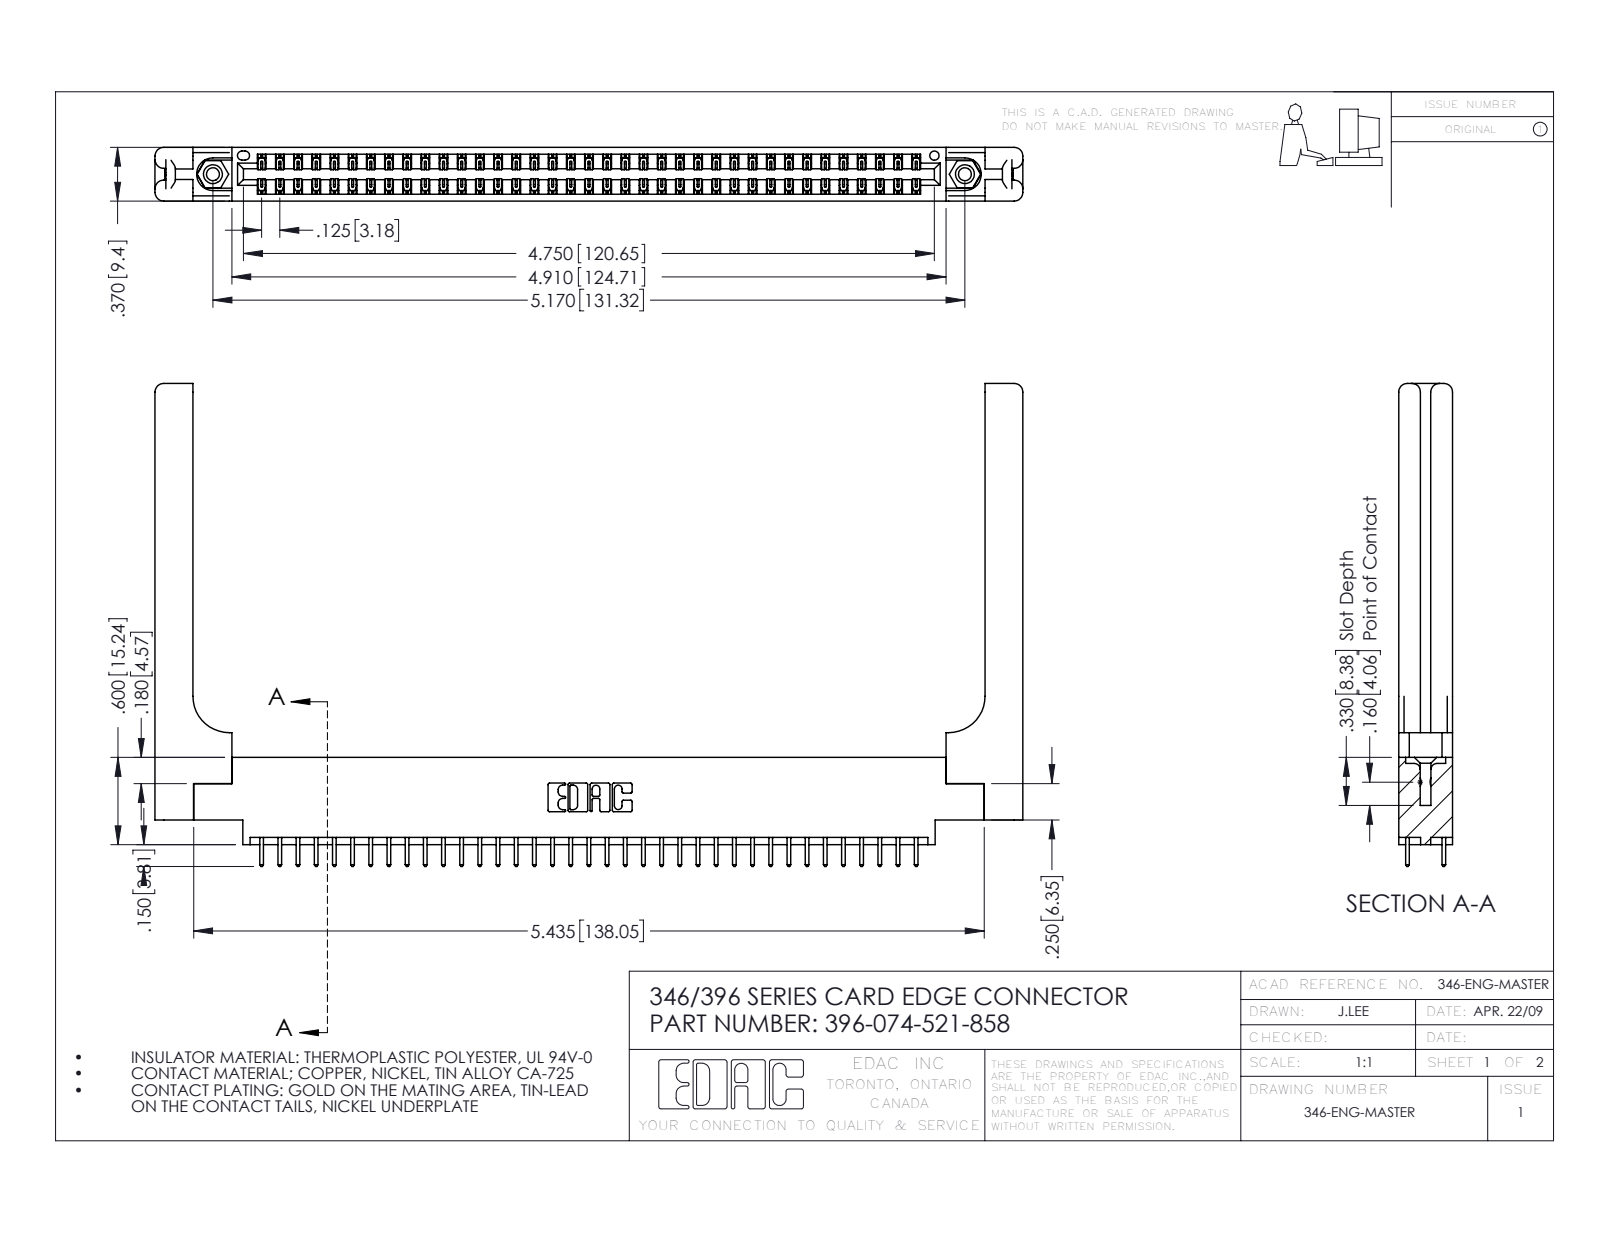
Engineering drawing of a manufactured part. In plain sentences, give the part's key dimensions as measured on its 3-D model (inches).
The part is named "345-250-001_345-250-001-102; 396-074-521-858; 345-292-001_345-293-121; 346 Part_0.170 Offset - 0.156 Dia-TH (+1 more)". Its 3-D file was written by "SolidWorks 2016 (CONFIG_CONTROL_DESIGN)". It is 79 solids with 4230 faces: 2818 planar, 1352 cylindrical and 60 other. Overall it measures 5.966 by 3.32 by 0.37 inches. Its volume is 1.345 cubic inches and its surface area 38.56 square inches. Round holes: 2 of diameter 0.089, 2 of diameter 0.125, 2 of diameter 0.156, 1 of diameter 0.064. Round bosses or shafts: 2 of diameter 0.155. Partial cylindrical surfaces (rounded edges, fillets, slot ends): 111 of radius 0.006, 74 of radius 0.01, 22 of radius 0.01, 16 of radius 0.06, 6 of radius 0.007, 6 of radius 0.031, 3 of radius 0.026, 2 of radius 0.014. The main face-to-face distances are 0.37, 0.048, 0.322, 0.072, 0.148, 0.15, 0.25, 0.025, 0.298, 0.275. The hole center spacings are 0.246, 4.961, 5.17.
